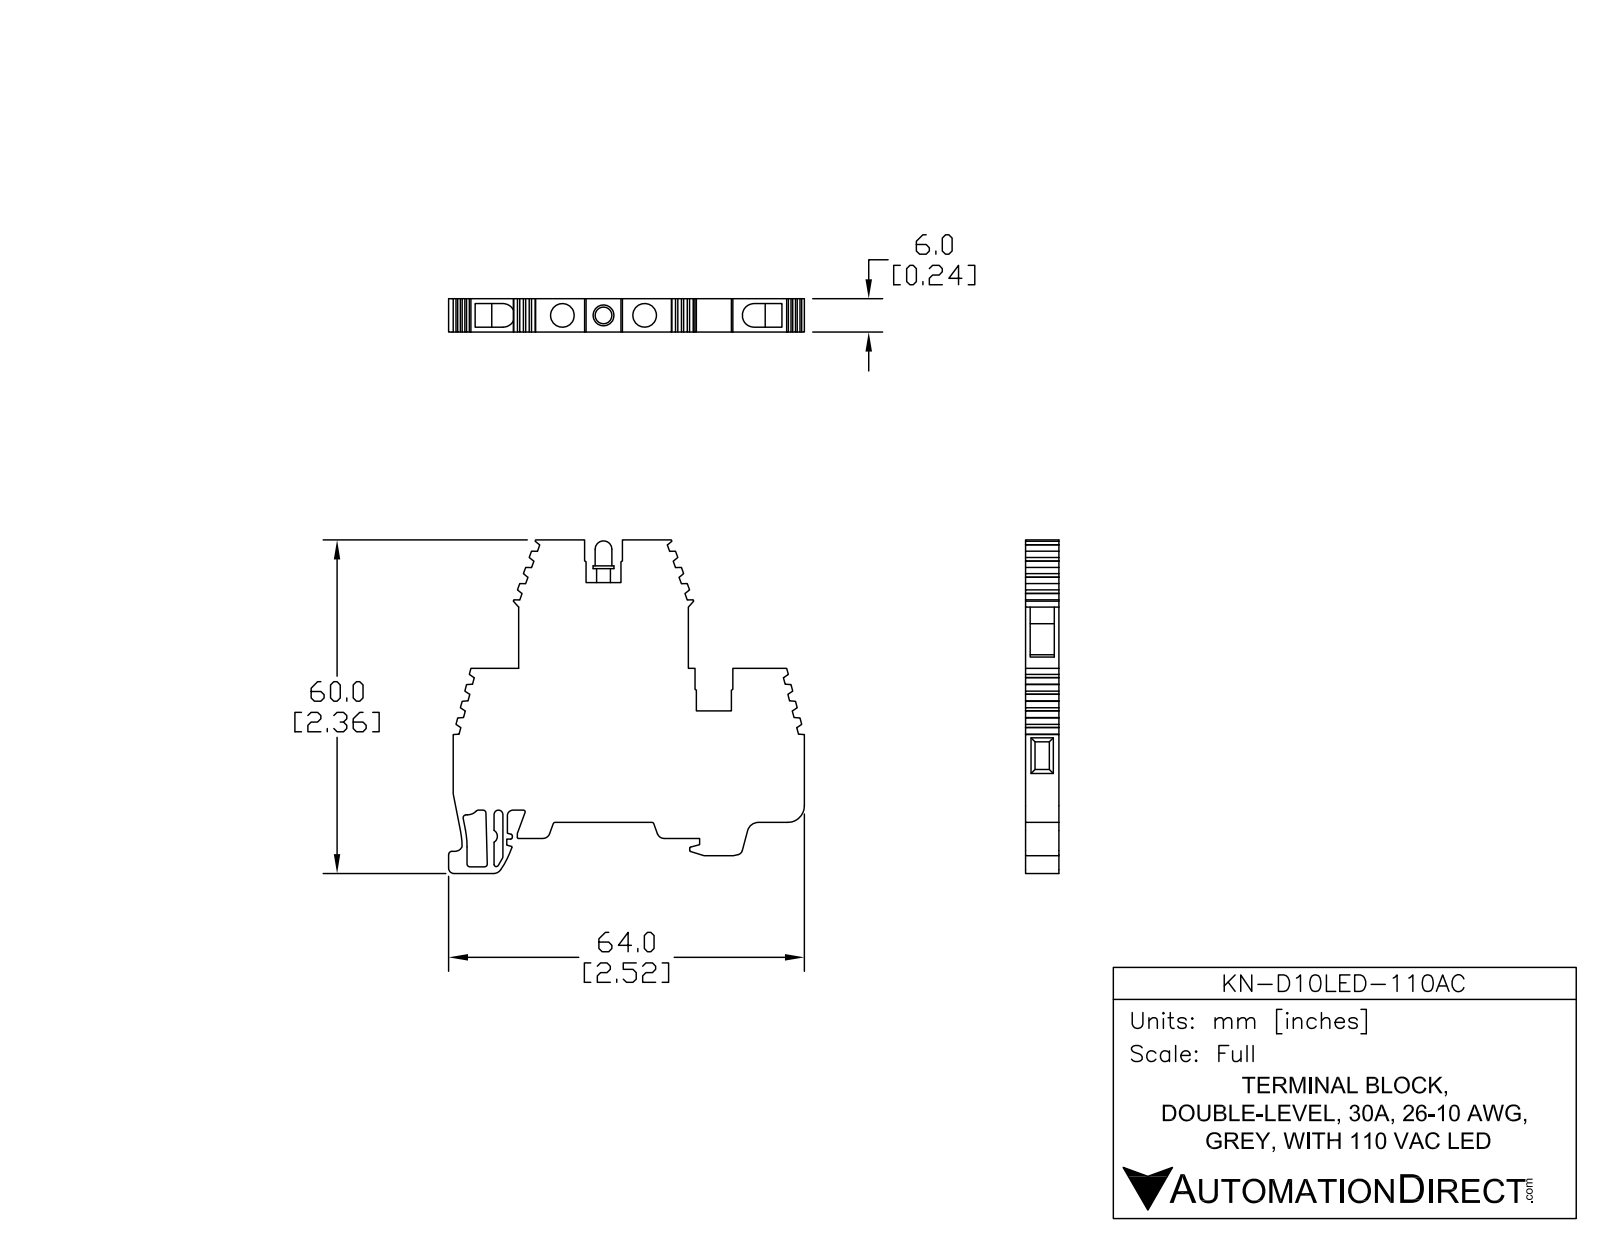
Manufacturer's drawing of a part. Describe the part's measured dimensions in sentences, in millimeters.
The part is named "KN-D10LED-110AC". Its 3-D file was written by "SolidWorks 2014 (AUTOMOTIVE_DESIGN)". It is 3 solids with 246 faces: 196 planar, 49 cylindrical and 1 other. Overall it measures 64.03 by 60 by 6 millimeters. Its volume is 13 705 cubic millimeters and its surface area 7 525 square millimeters. Round holes: 2 of diameter 4.25. Round bosses or shafts: 1 of diameter 3.75, 1 of diameter 3, 1 of diameter 2.5. Partial cylindrical surfaces (rounded edges, fillets, slot ends): 7 of radius 0.5, 6 of radius 0.3, 3 of radius 0.2, 3 of radius 1, 2 of radius 0.6, 2 of radius 2.12, 1 of radius 0.4, 1 of radius 0.8. The main face-to-face distances are 6, 5.17, 2.93, 0.83, 23.08, 6.55, 19.86, 6.3, 4, 7.67. The hole center spacings are 14.8.
